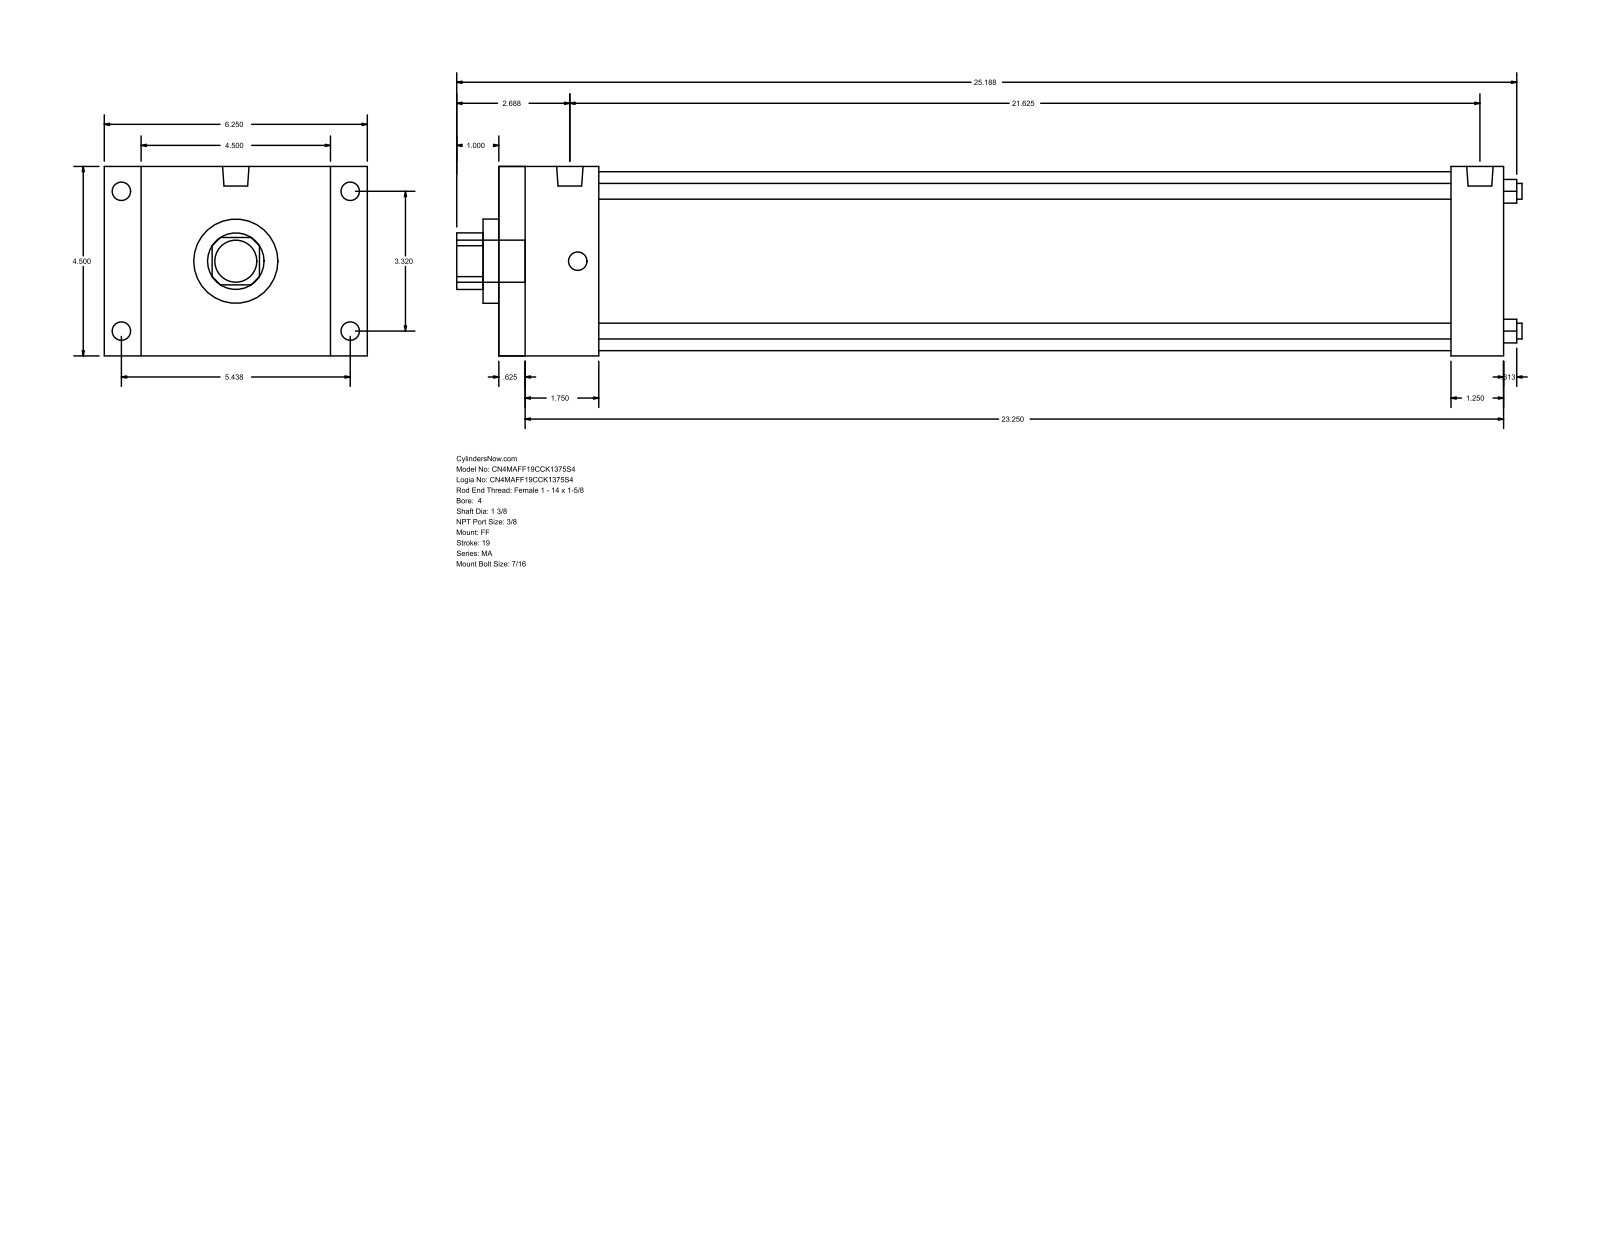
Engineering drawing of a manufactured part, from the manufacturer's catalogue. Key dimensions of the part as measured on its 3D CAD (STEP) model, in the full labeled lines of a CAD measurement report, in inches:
Part name (STEP PRODUCT): MA_FF__0400_1.375
STEP written by: GSSL Pune (CONFIG_CONTROL_DESIGN)
Units: inches
Bodies: 0 solids, 92 faces (64 planar, 28 cylindrical, 0 other)
Overall size (bounding box): 25.313 × 6.25 × 4.5
Round holes (diameter × count): ⌀0.375 ×4, ⌀1.375 ×1, ⌀2 ×1, ⌀4.25 ×1
Round bosses / shafts (diameter × count): ⌀0.437 ×8, ⌀0.627 ×2, ⌀1 ×1
Partial cylindrical surfaces — rounded edges, fillets, slot ends (radius × count): R0.672 ×1
Main face-to-face distances: 4.5, 23.875, 0.625, 23.25, 0.875, 5.375, 22.625, 22, 1.25, 2.375
Hole centre spacings: 2.347, 3.32, 4.695
